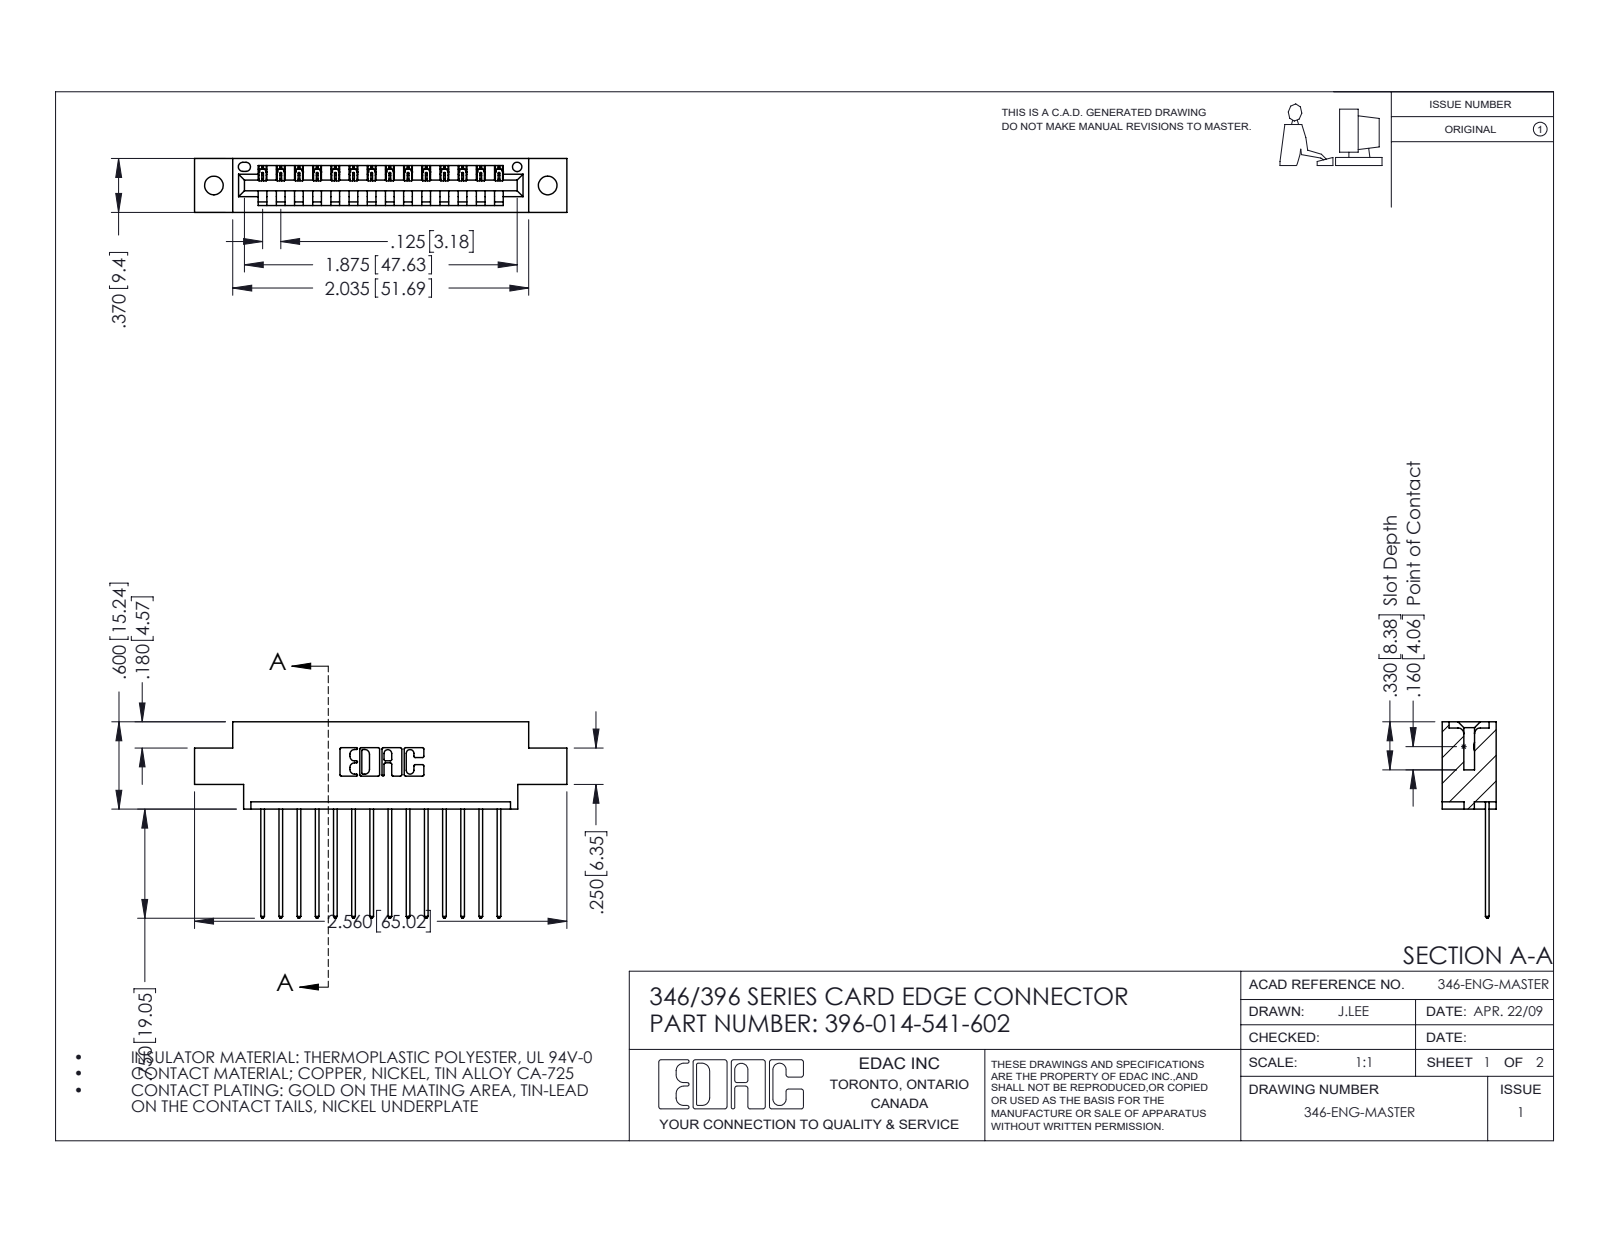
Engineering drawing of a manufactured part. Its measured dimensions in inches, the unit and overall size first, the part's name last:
Units: inches
Overall size (bounding box): 2.56 × 1.35 × 0.37
Round holes (diameter × count): ⌀0.128 ×2, ⌀0.064 ×1
Partial cylindrical surfaces — rounded edges, fillets, slot ends (radius × count): R0.006 ×28, R0.01 ×28, R0.01 ×22, R0.007 ×6, R0.031 ×6, R0.026 ×3, R0.031 ×2, R0.04 ×2
Main face-to-face distances: 0.048, 0.322, 0.37, 0.25, 0.072, 0.298, 0.025, 0.148, 0.222, 0.1
Hole centre spacings: 0.246, 2.089, 2.295
Volume: 0.359 in³ · Surface area: 11.19 in²
Bodies: 15 solids, 938 faces (640 planar, 298 cylindrical, 0 other)
Part name (STEP PRODUCT): 345-292-001_345-293-141; 346 Part_0.170 Offset - 0.128 Dia; 396-014-541-602
STEP written by: SolidWorks 2016 (CONFIG_CONTROL_DESIGN)
